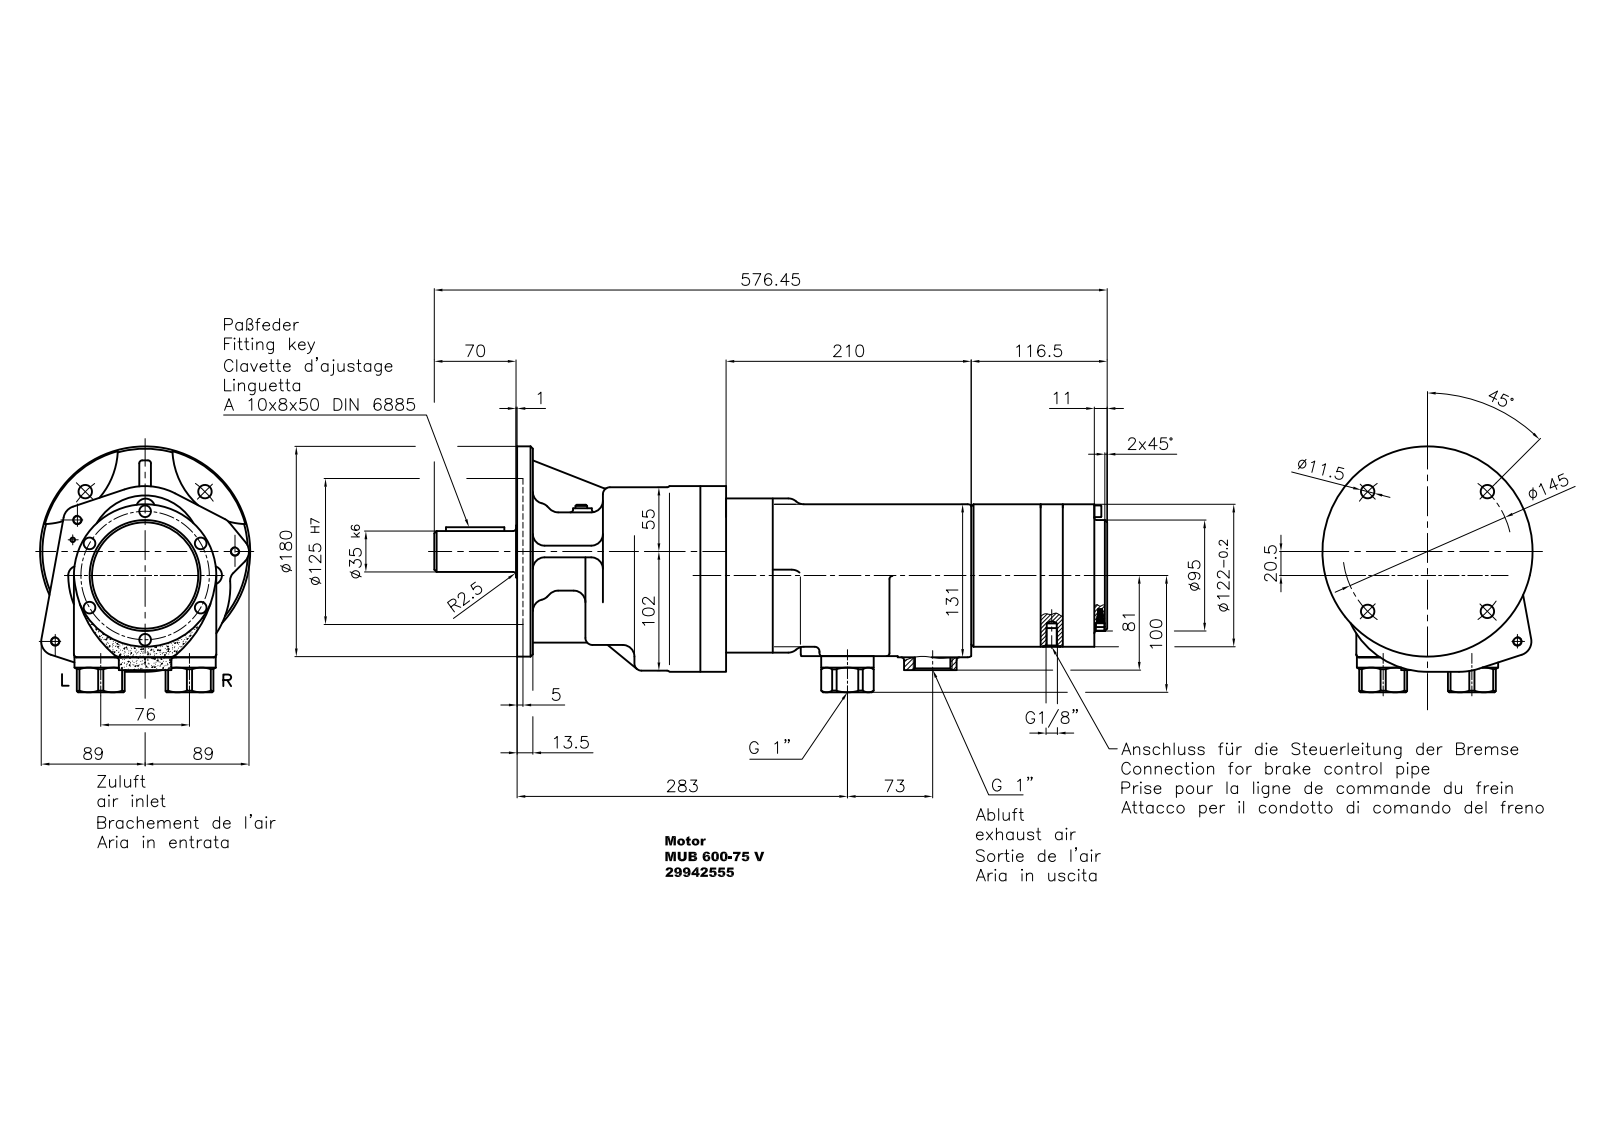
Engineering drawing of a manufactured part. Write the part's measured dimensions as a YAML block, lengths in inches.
part_name: "MUB 600-75 V"
step_written_by: "Autodesk Inventor 2008 (AUTOMOTIVE_DESIGN)"
units: inches
bodies: {solids: 1, faces: 1412, planar: 519, cylindrical: 469, other: 424}
overall_size: [22.715, 8.093, 7.087]
volume: 364.3
surface_area: 846.3
round_holes:
  - {diameter: 0.453, count: 4}
  - {diameter: 0.335, count: 3}
  - {diameter: 0.374, count: 3}
  - {diameter: 0.276, count: 2}
  - {diameter: 0.709, count: 2}
  - {diameter: 1.309, count: 2}
  - {diameter: 0.094, count: 1}
  - {diameter: 0.098, count: 1}
  - {diameter: 0.11, count: 1}
  - {diameter: 0.197, count: 1}
  - {diameter: 0.311, count: 1}
  - {diameter: 1.181, count: 1}
round_bosses_or_shafts:
  - {diameter: 0.184, count: 17}
  - {diameter: 0.394, count: 7}
  - {diameter: 0.236, count: 6}
  - {diameter: 0.583, count: 3}
  - {diameter: 0.512, count: 3}
  - {diameter: 0.315, count: 3}
  - {diameter: 1.772, count: 2}
  - {diameter: 1.614, count: 2}
partial_cylinders:
  - {radius: 0.098, count: 34}
  - {radius: 0.079, count: 32}
  - {radius: 0.157, count: 23}
  - {radius: 0.236, count: 14}
  - {radius: 0.394, count: 13}
  - {radius: 0.197, count: 11}
  - {radius: 0.472, count: 8}
  - {radius: 1.119, count: 8}
face_to_face_distances: [0.197, 6.87, 7.067, 1.398, 5.472, 5.669, 0.039, 0.335, 6.535, 5.137]
hole_center_spacings: [2.855, 4.037, 0.687, 1.43, 2.258, 2.283, 2.364, 2.459]
